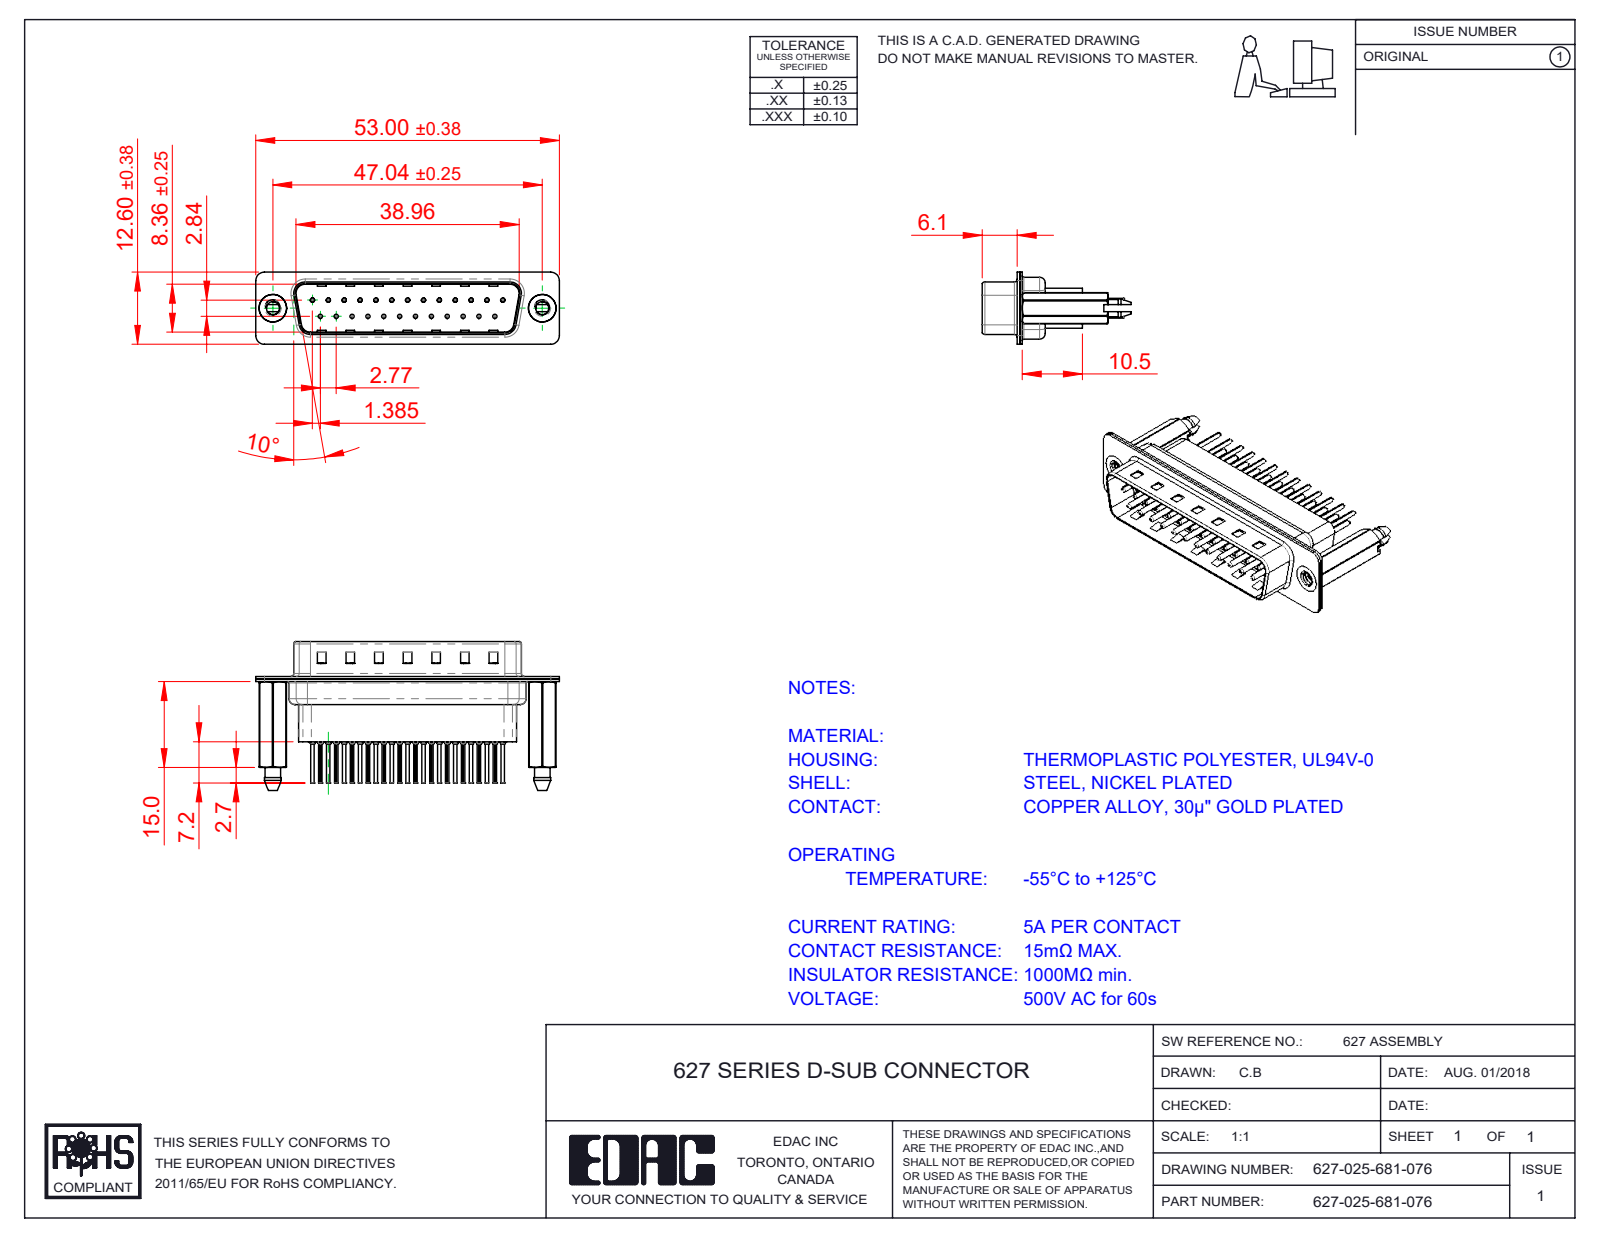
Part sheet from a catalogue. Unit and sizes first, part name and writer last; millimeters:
Units: millimetres
Overall size (bounding box): 53 × 25.9 × 12.6
Round holes (diameter × count): ⌀0.2 ×25, ⌀0.35 ×25, ⌀1.1 ×25, ⌀1.6 ×25, ⌀2.26 ×2, ⌀4 ×2, ⌀4.8 ×2
Round bosses / shafts (diameter × count): ⌀2 ×25, ⌀1.5 ×25, ⌀0.75 ×25, ⌀0.6 ×25, ⌀4.9 ×2
Partial cylindrical surfaces — rounded edges, fillets, slot ends (radius × count): R0.1 ×50, R1.5 ×18, R2 ×12, R1.6 ×10, R0.5 ×8, R0.25 ×4, R0.6 ×4, R0.65 ×4
Main face-to-face distances: 0.4, 0.45, 0.82, 9.58, 0.68, 7.68, 1.5, 0.9, 1.08, 8.08
Hole centre spacings: 3.16, 8.31, 2.77, 5.54, 11.08, 16.62, 5.03, 5.04
Volume: 4 205 mm³ · Surface area: 10 831 mm²
Bodies: 30 solids, 2934 faces (803 planar, 1128 cylindrical, 1003 other)
Part name (STEP PRODUCT): 627 Housing_25 HP; 627 Shell Rear_25 Contacts; 627-025-681-076; 627 Contact Row 2_61 (+3 more)
STEP written by: SolidWorks 2020 (CONFIG_CONTROL_DESIGN)
